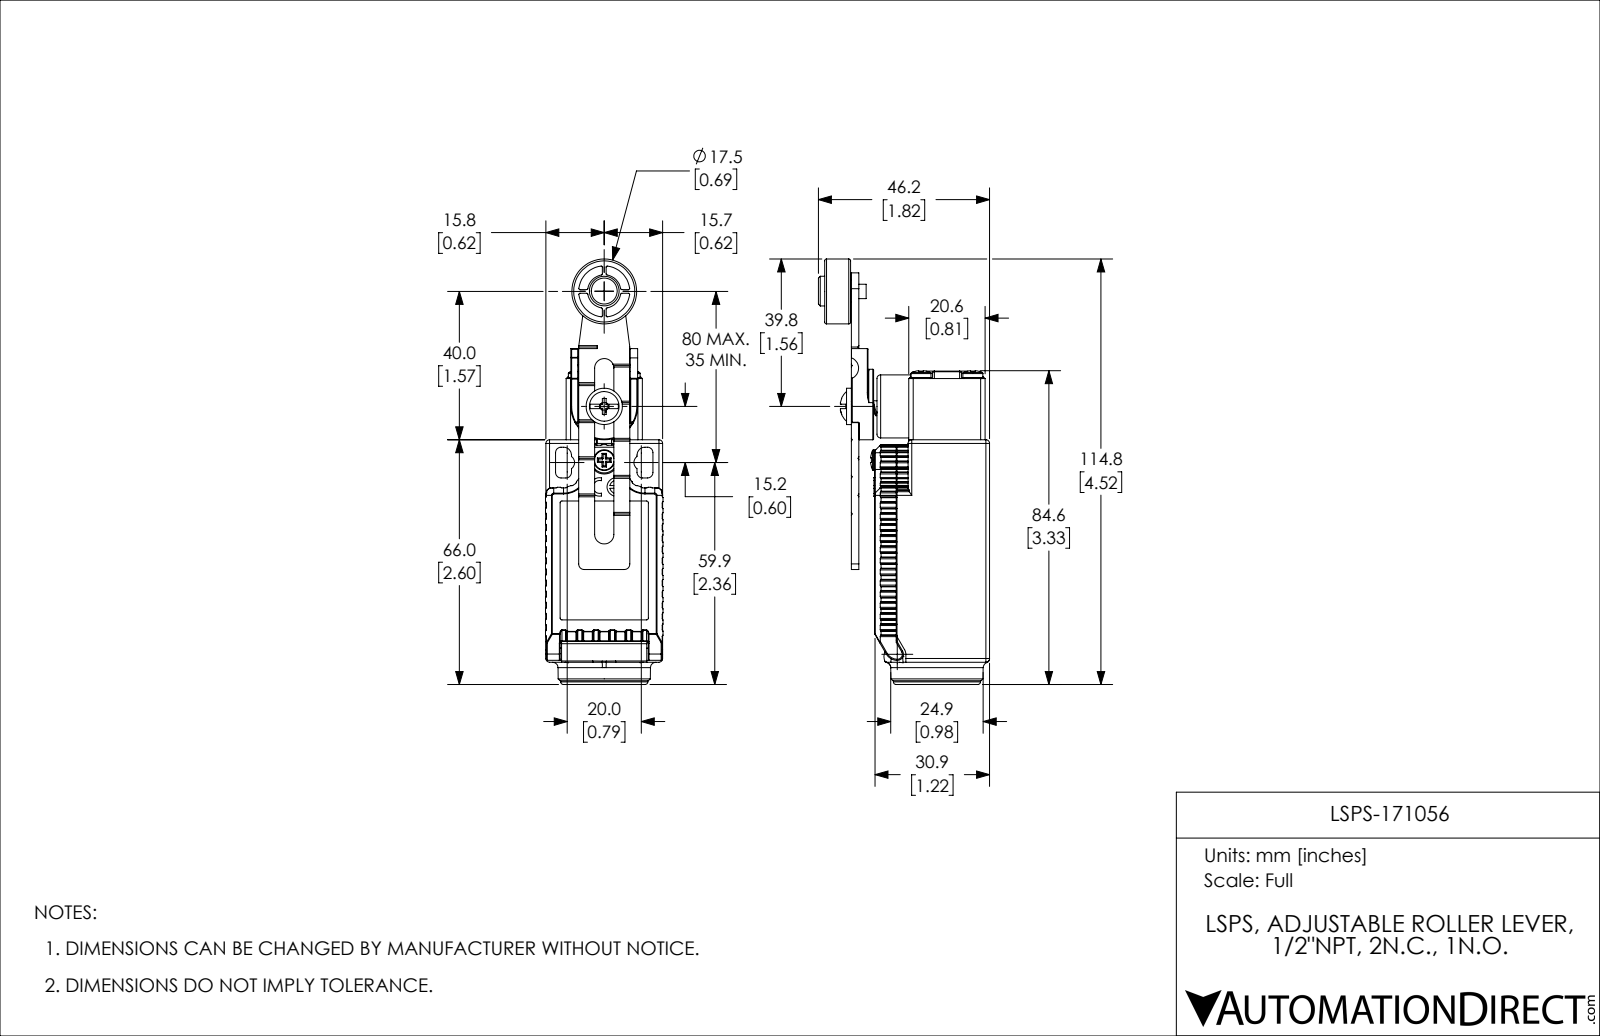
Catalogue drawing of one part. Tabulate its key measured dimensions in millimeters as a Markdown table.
| quantity | value |
| --- | --- |
| part name | 171-LSPS-Adjustable Roller Lever (STEP format) |
| STEP written by | SolidWorks 2015 (CONFIG_CONTROL_DESIGN) |
| units | millimeters |
| bodies | 14 solids, 2663 faces (1176 planar, 1120 cylindrical, 367 other) |
| overall size | 114.75 × 46.2 × 31.7 |
| volume | 32 834 mm³ |
| surface area | 34 545 mm² |
| round holes (diameter × count) | 2.3 × 5, 2.8 × 4, 3.2 × 4, 5.5 × 4, 4 × 2, 2.9 × 1, 4.1 × 1, 5 × 1, 6.1 × 1, 7.2 × 1, 8 × 1, 9.8 × 1 |
| round bosses / shafts (diameter × count) | 1.7 × 5, 5.4 × 4, 2.5 × 4, 23.5 × 1, 17.7 × 1, 17.5 × 1, 17 × 1, 10 × 1 |
| partial cylindrical surfaces (radius × count) | 0.2 × 138, 0.5 × 129, 0.1 × 92, 0.3 × 69, 0.34 × 32, 1 × 23, 2 × 18, 0.8 × 16 |
| main face-to-face distances | 4.5, 29.25, 2.25, 2, 31.5, 1, 3.2, 9.5, 1.6, 27 |
| hole center spacings | 9.9, 14, 7.76, 8.22, 11.96, 16.4, 19.8, 20 |
